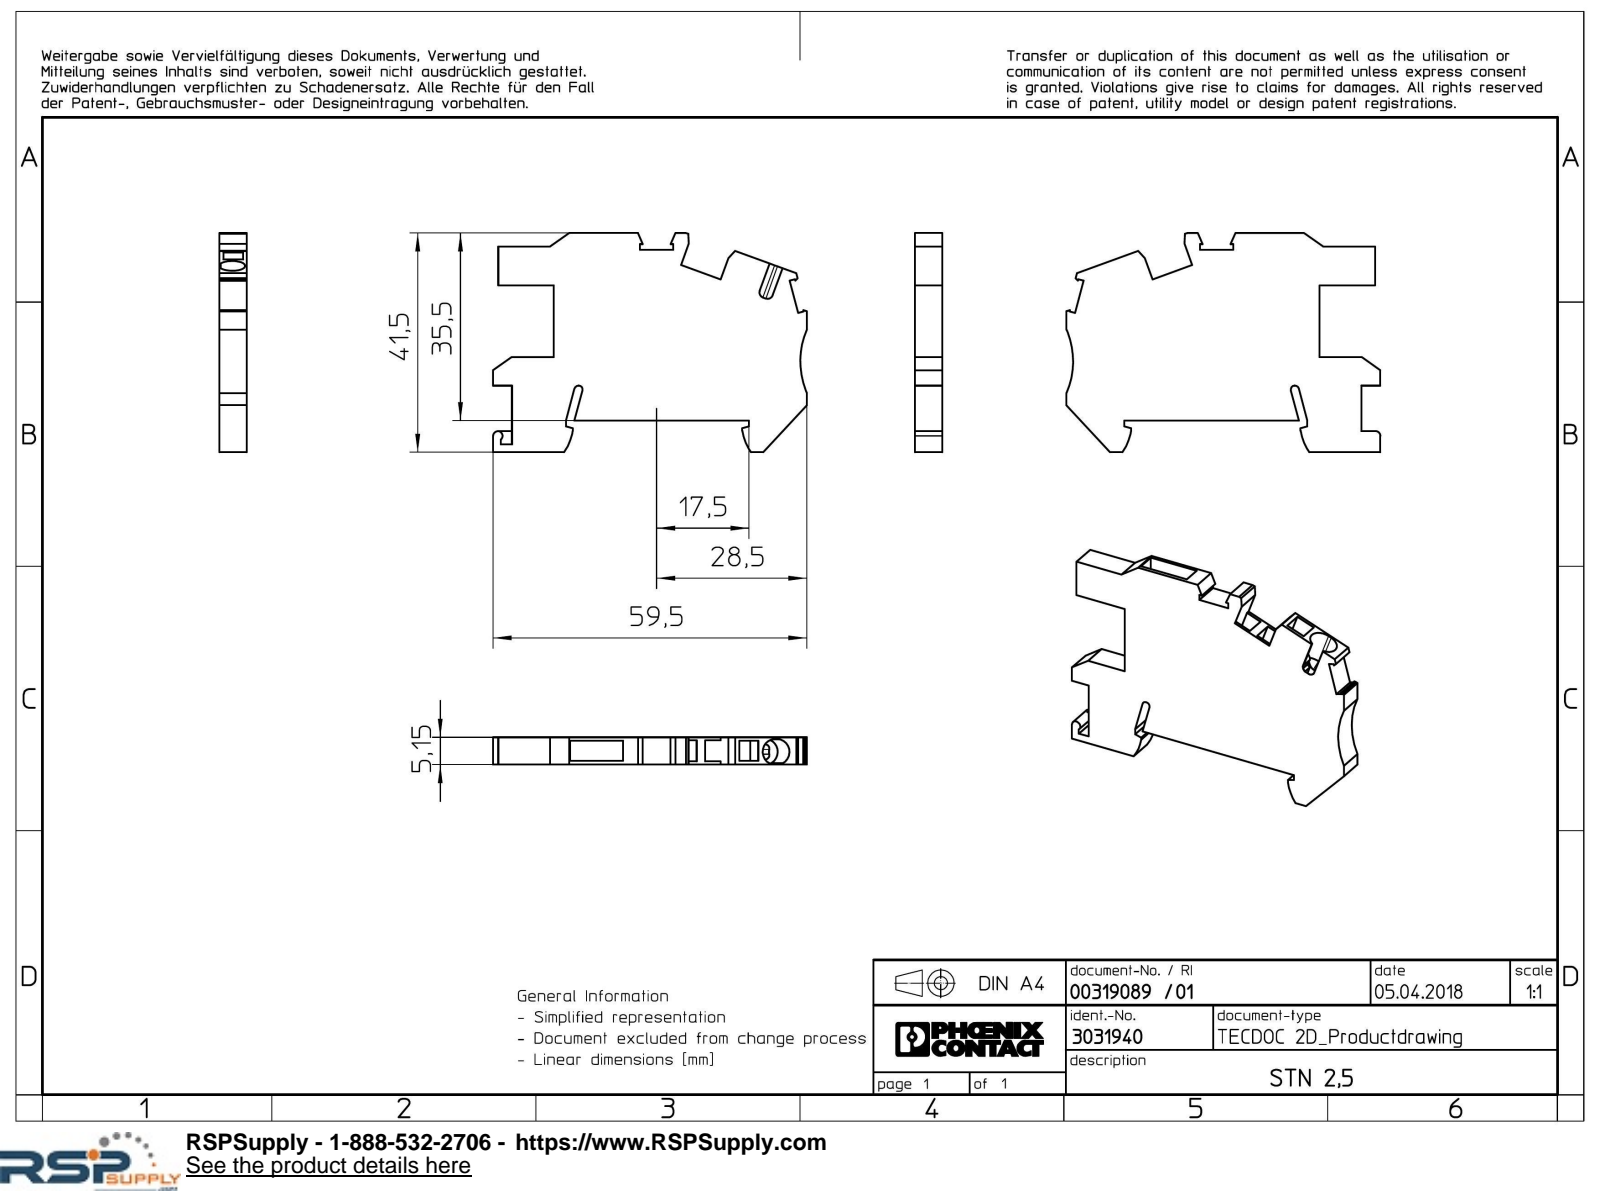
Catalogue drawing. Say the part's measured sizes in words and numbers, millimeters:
The part is named "STN-2.5-SELECT". Its 3-D file was written by "Creo Elements/Direct Modeling 18.1I 14-Aug-2016 (C) Parametric Technology GmbH (AUTOMOTIVE_DESIGN)". It is 1 solid with 103 faces: 88 planar, 12 cylindrical and 3 other. Overall it measures 59.45 by 41.5 by 5.15 millimeters. Its volume is 8 430 cubic millimeters and its surface area 5 713 square millimeters. Partial cylindrical surfaces (rounded edges, fillets, slot ends): 4 of radius 1, 2 of radius 2.4, 2 of radius 9.5, 1 of radius 0.7, 1 of radius 0.8, 1 of radius 0.9, 1 of radius 15. The main face-to-face distances are 5.15, 6, 0.65, 3.15, 4.5, 4, 4.57, 0.58, 0.57, 4.58.
